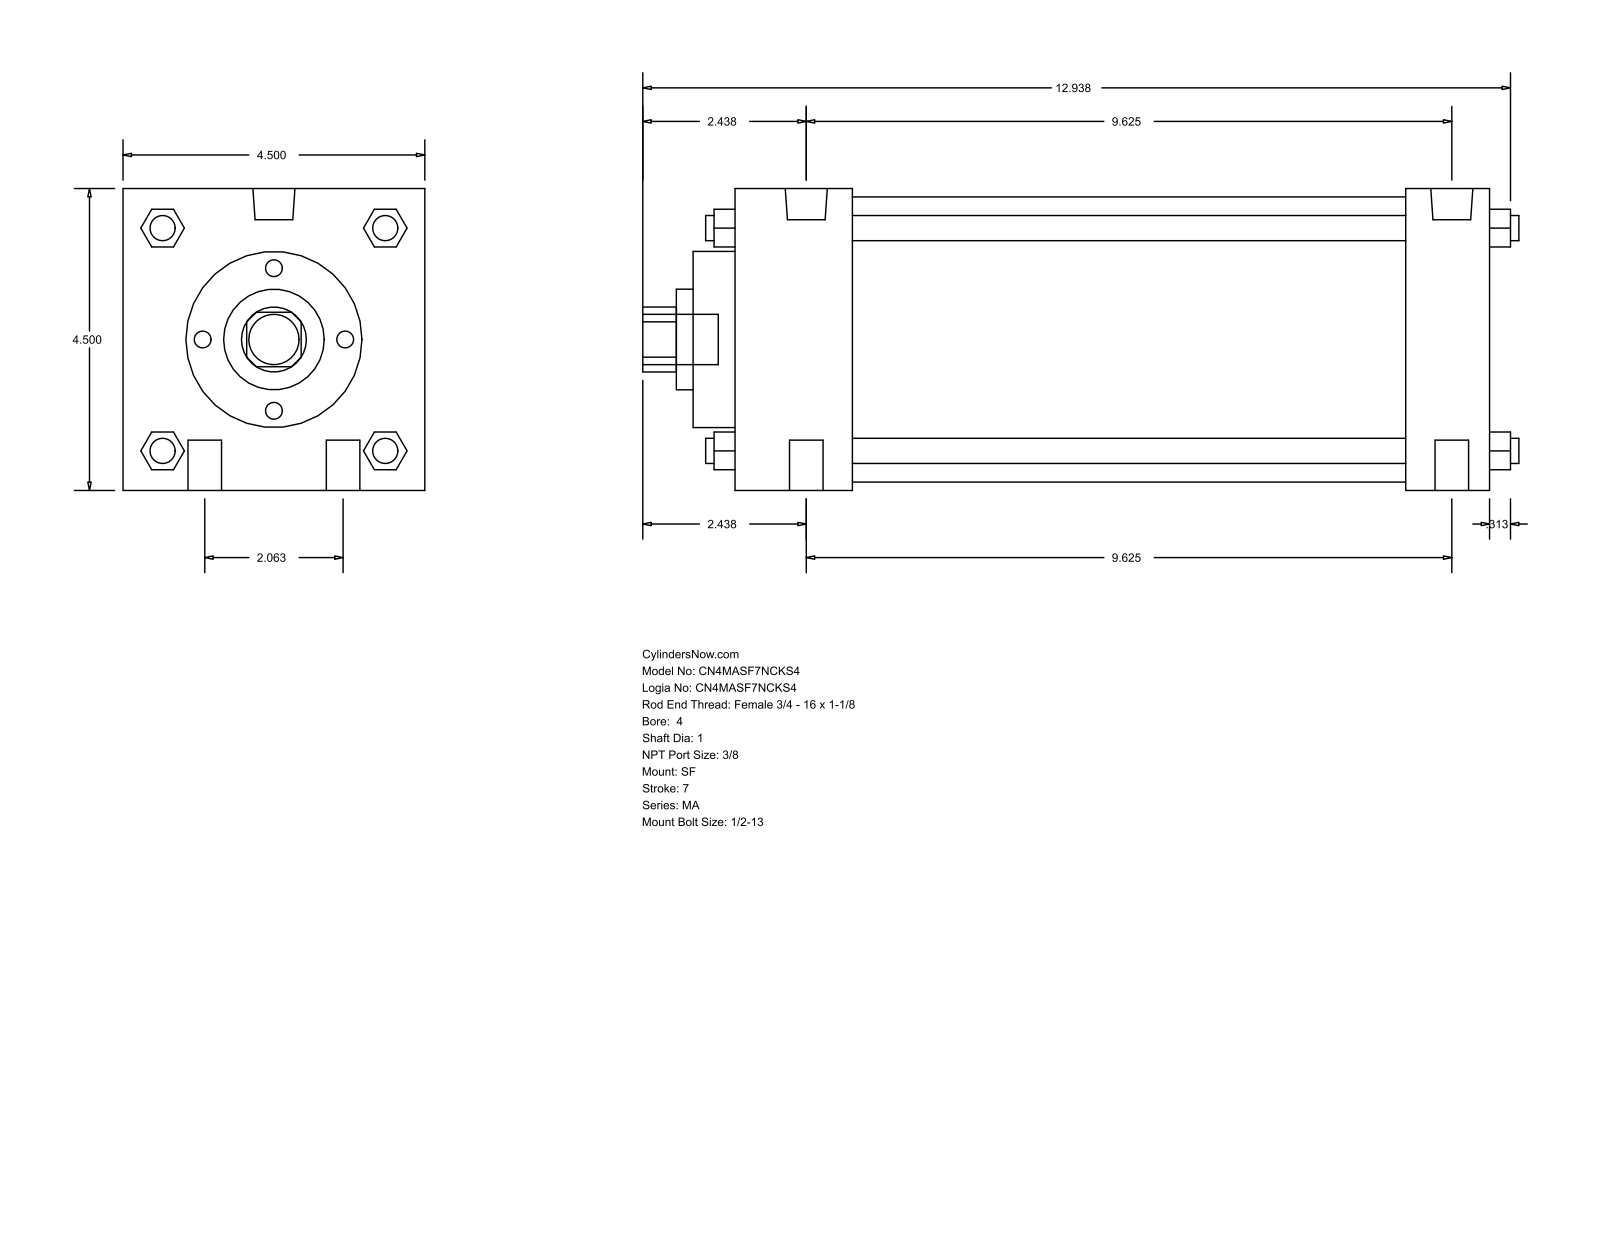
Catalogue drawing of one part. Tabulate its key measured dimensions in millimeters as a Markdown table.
| quantity | value |
| --- | --- |
| part name | MA_SF__0400_1 |
| STEP written by | GSSL Pune (CONFIG_CONTROL_DESIGN) |
| units | millimeters |
| bodies | 0 solids, 126 faces (95 planar, 31 cylindrical, 0 other) |
| overall size | 331.79 × 114.3 × 114.3 |
| round holes (diameter × count) | 25.4 × 1, 38.1 × 1, 66.67 × 1, 107.95 × 1 |
| round bosses / shafts (diameter × count) | 12.7 × 4, 9.53 × 4, 15.93 × 2, 11.11 × 2, 19.05 × 1 |
| partial cylindrical surfaces (radius × count) | 12.29 × 1 |
| main face-to-face distances | 114.3, 285.76, 254.01, 31.75, 44.46, 209.55, 241.3, 15.87, 60.33, 269.88 |
